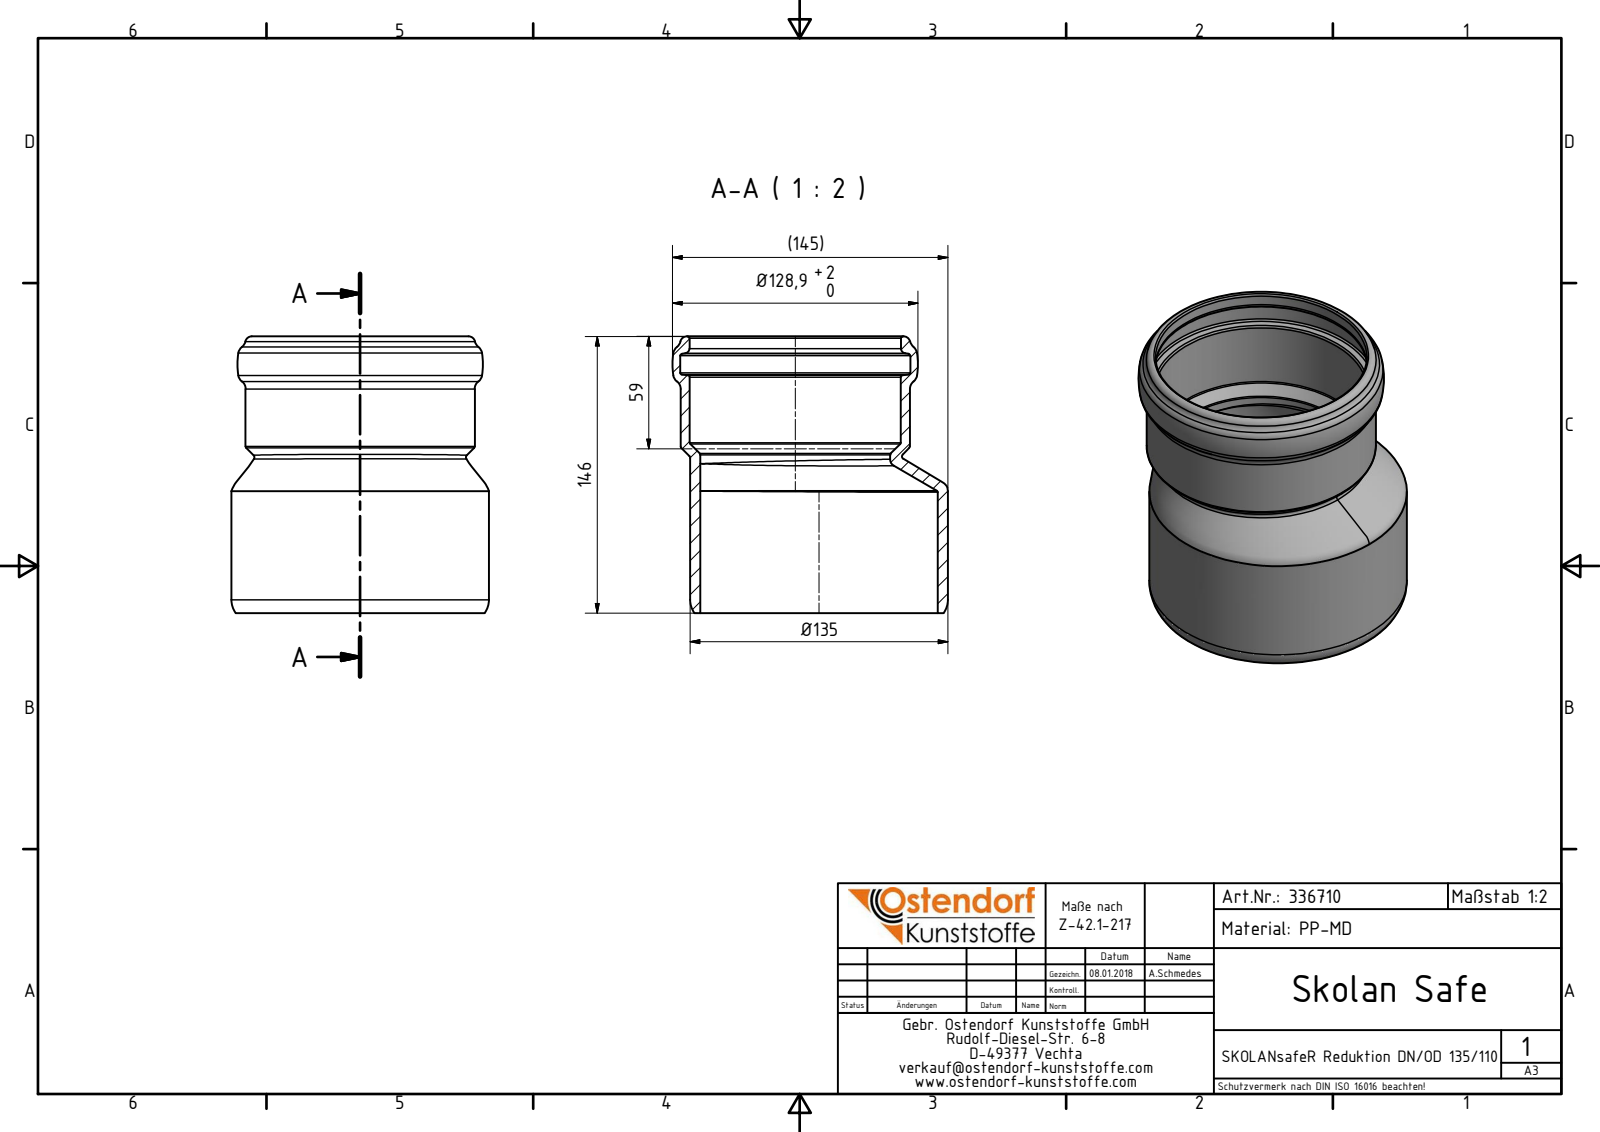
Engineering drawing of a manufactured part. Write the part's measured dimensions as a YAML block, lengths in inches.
part_name: "336710 SKOLANsafeR Reduktion DN_OD 135_110"
step_written_by: "Autodesk Inventor 2016 (AUTOMOTIVE_DESIGN)"
units: inches
bodies: {solids: 1, faces: 32, planar: 1, cylindrical: 7, other: 24}
overall_size: [5.719, 5.693, 5.327]
volume: 18.51
surface_area: 191.3
round_holes:
  - {diameter: 3.925, count: 1}
  - {diameter: 4.362, count: 1}
  - {diameter: 4.37, count: 1}
  - {diameter: 4.76, count: 1}
  - {diameter: 4.909, count: 1}
round_bosses_or_shafts:
  - {diameter: 5.327, count: 1}
  - {diameter: 4.74, count: 1}
hole_center_spacings: [0.492]
